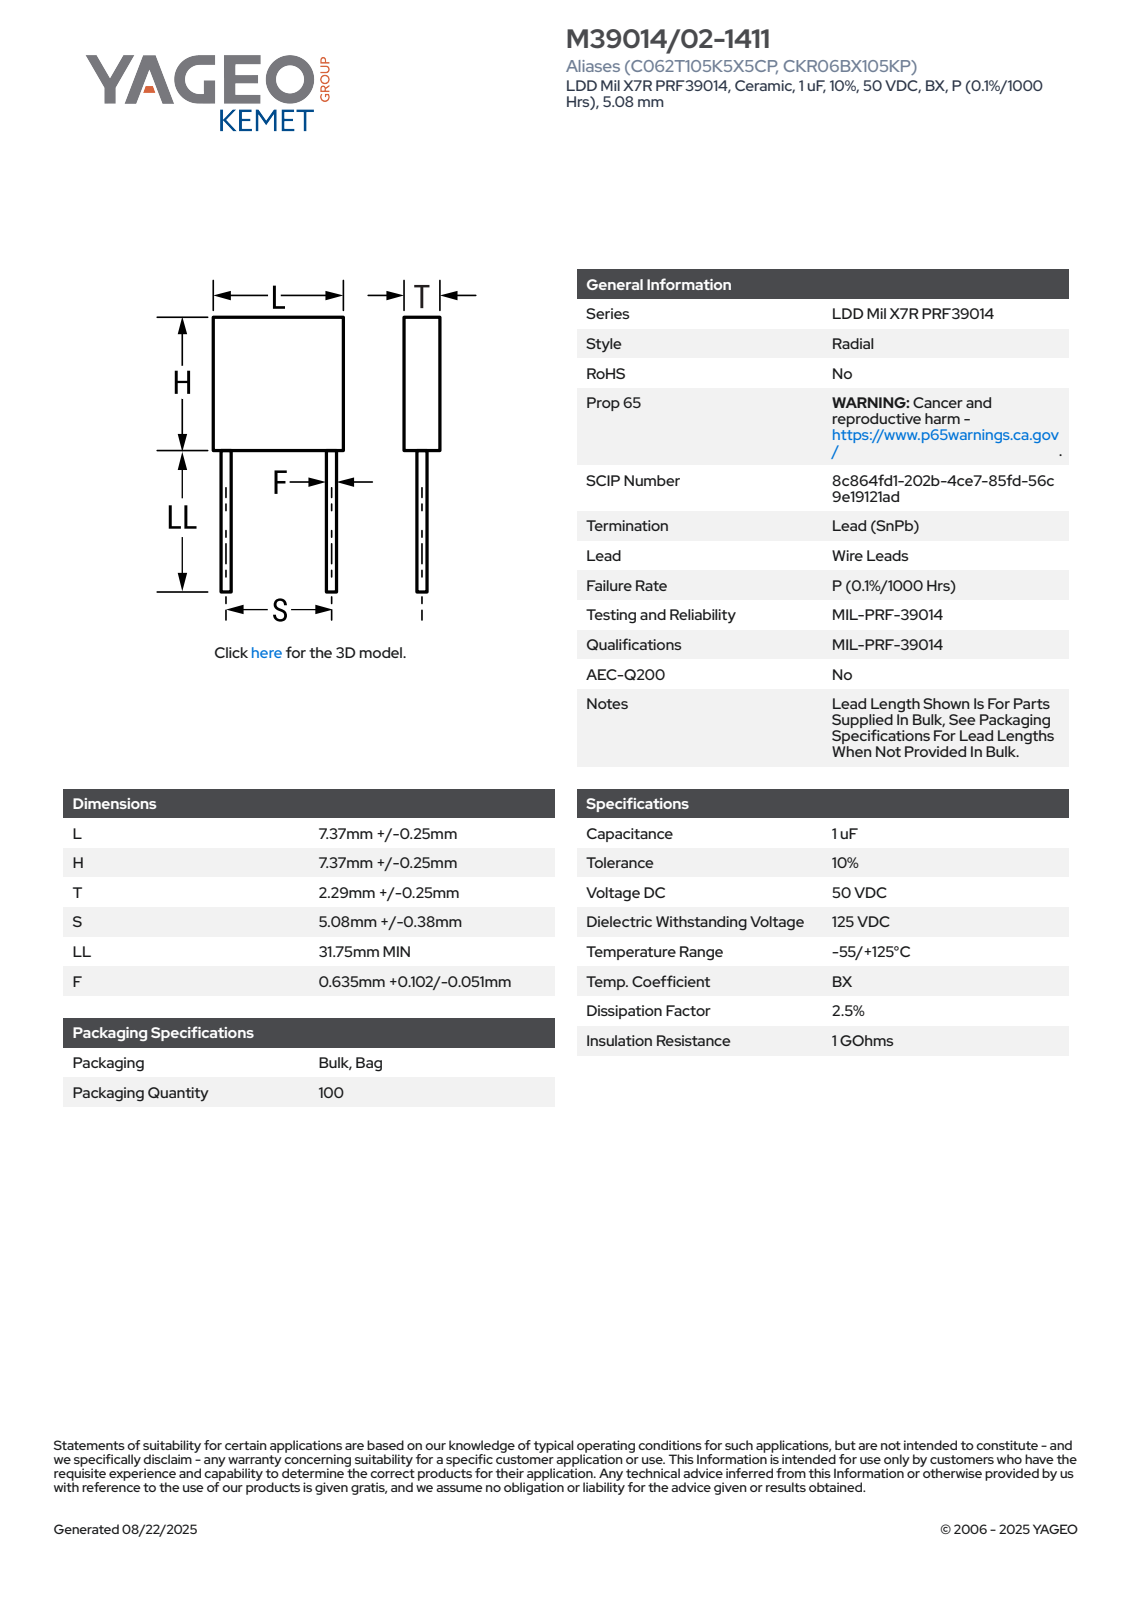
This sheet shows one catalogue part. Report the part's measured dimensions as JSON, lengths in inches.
{"part_name": "CCRM_ST_C062_L7.62H7.62T2.54S5.08LL31.75F0.737", "step_written_by": "SolidWorks 2021 (AUTOMOTIVE_DESIGN)", "units": "inches", "bodies": {"solids": 4, "faces": 69, "planar": 65, "cylindrical": 4, "other": 0}, "overall_size": [1.55, 0.3, 0.1], "volume_in3": 0.011, "surface_area_in2": 0.543, "round_bosses_or_shafts": [[0.029, 2]], "face_to_face_distances": [0.1, 0.3, 1.25, 1.55, 0.126, 0.174, 1.424, 1.376, 0.049, 0.013]}
